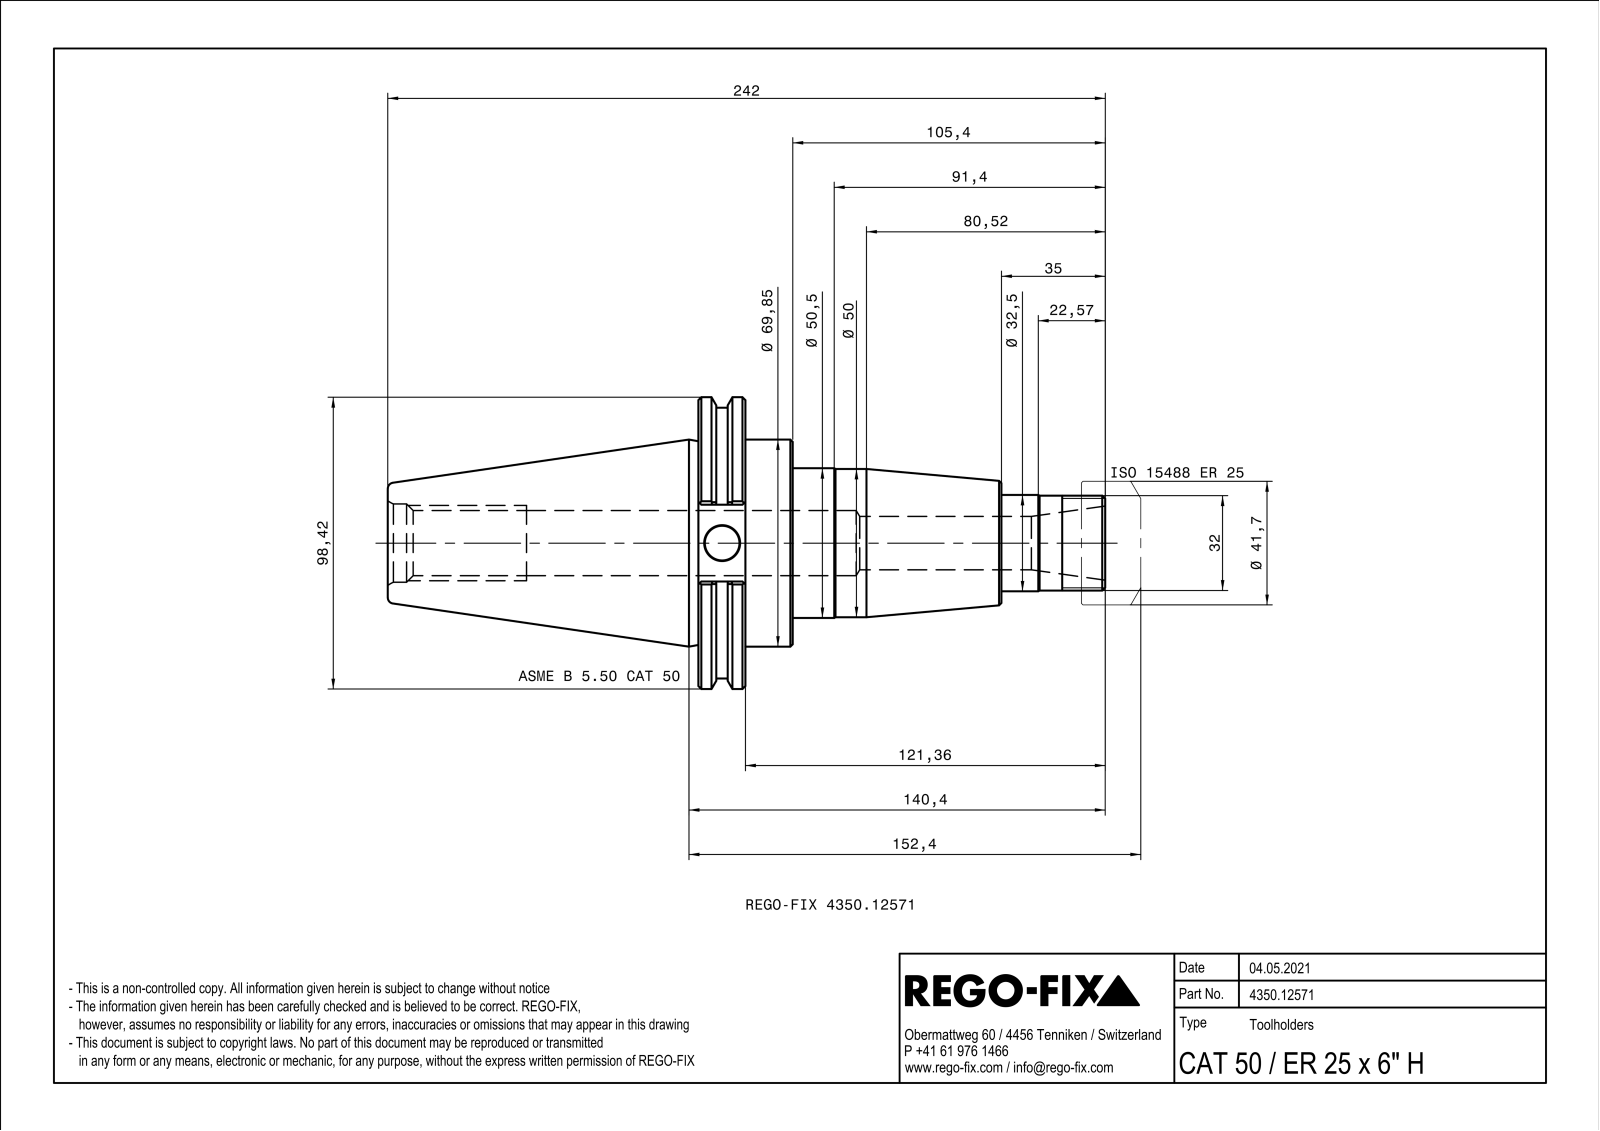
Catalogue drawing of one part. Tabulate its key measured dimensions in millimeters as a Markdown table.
| quantity | value |
| --- | --- |
| part name | NOCUT |
| STEP written by | SIEMENS PLM Software Solid Edge ST10 (AUTOMOTIVE_DESIGN) |
| units | millimeters |
| bodies | 1 solid, 124 faces (32 planar, 34 cylindrical, 58 other) |
| overall size | 242 × 98.42 × 94.39 |
| volume | 492 951 mm³ |
| surface area | 68 246 mm² |
| round holes (diameter × count) | 11.7 × 1, 18 × 1, 21.96 × 1, 21.96 × 1, 26.4 × 1 |
| round bosses / shafts (diameter × count) | 98.42 × 1, 91.3 × 1, 69.85 × 1, 50.5 × 1, 50 × 1, 32.5 × 1, 32 × 1 |
| partial cylindrical surfaces (radius × count) | 0.5 × 12 |
| main face-to-face distances | 15.87, 15.96, 31.83, 136.6, 120.64, 104.77, 70.4, 86.36, 102.23, 207 |
